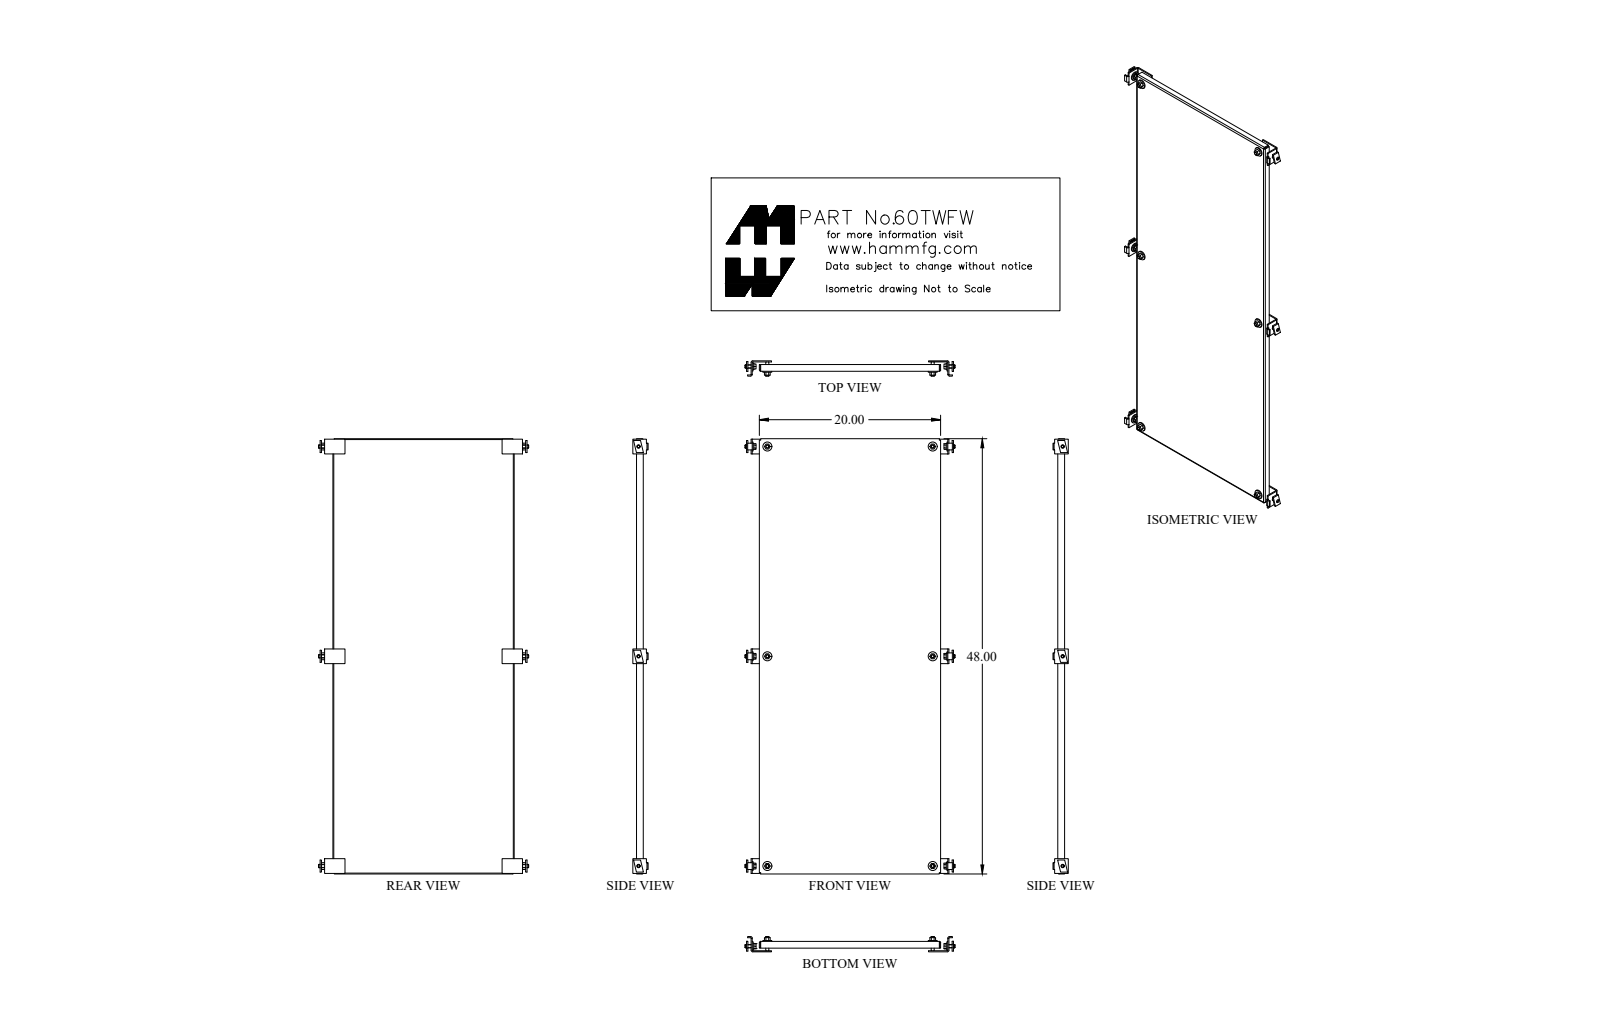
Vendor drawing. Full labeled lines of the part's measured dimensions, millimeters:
Part name (STEP PRODUCT): 60TWFW_Default
STEP written by: SolidWorks 2018 (CONFIG_CONTROL_DESIGN)
Units: millimetres
Bodies: 1 solid, 42 faces (22 planar, 20 cylindrical, 0 other)
Overall size (bounding box): 1219.2 × 508 × 19.1
Volume: 1 621 000 mm³ · Surface area: 1 353 000 mm²
Round holes (diameter × count): ⌀14.3 ×6
Partial cylindrical surfaces — rounded edges, fillets, slot ends (radius × count): R1.2 ×4, R3.6 ×4
Main face-to-face distances: 2.4, 505.6, 503.2, 508, 1216.8, 19.1, 16.6, 1219.2, 1214.4, 3.6
Hole centre spacings: 587.4, 748.3, 463.6, 1174.8, 1262.9
